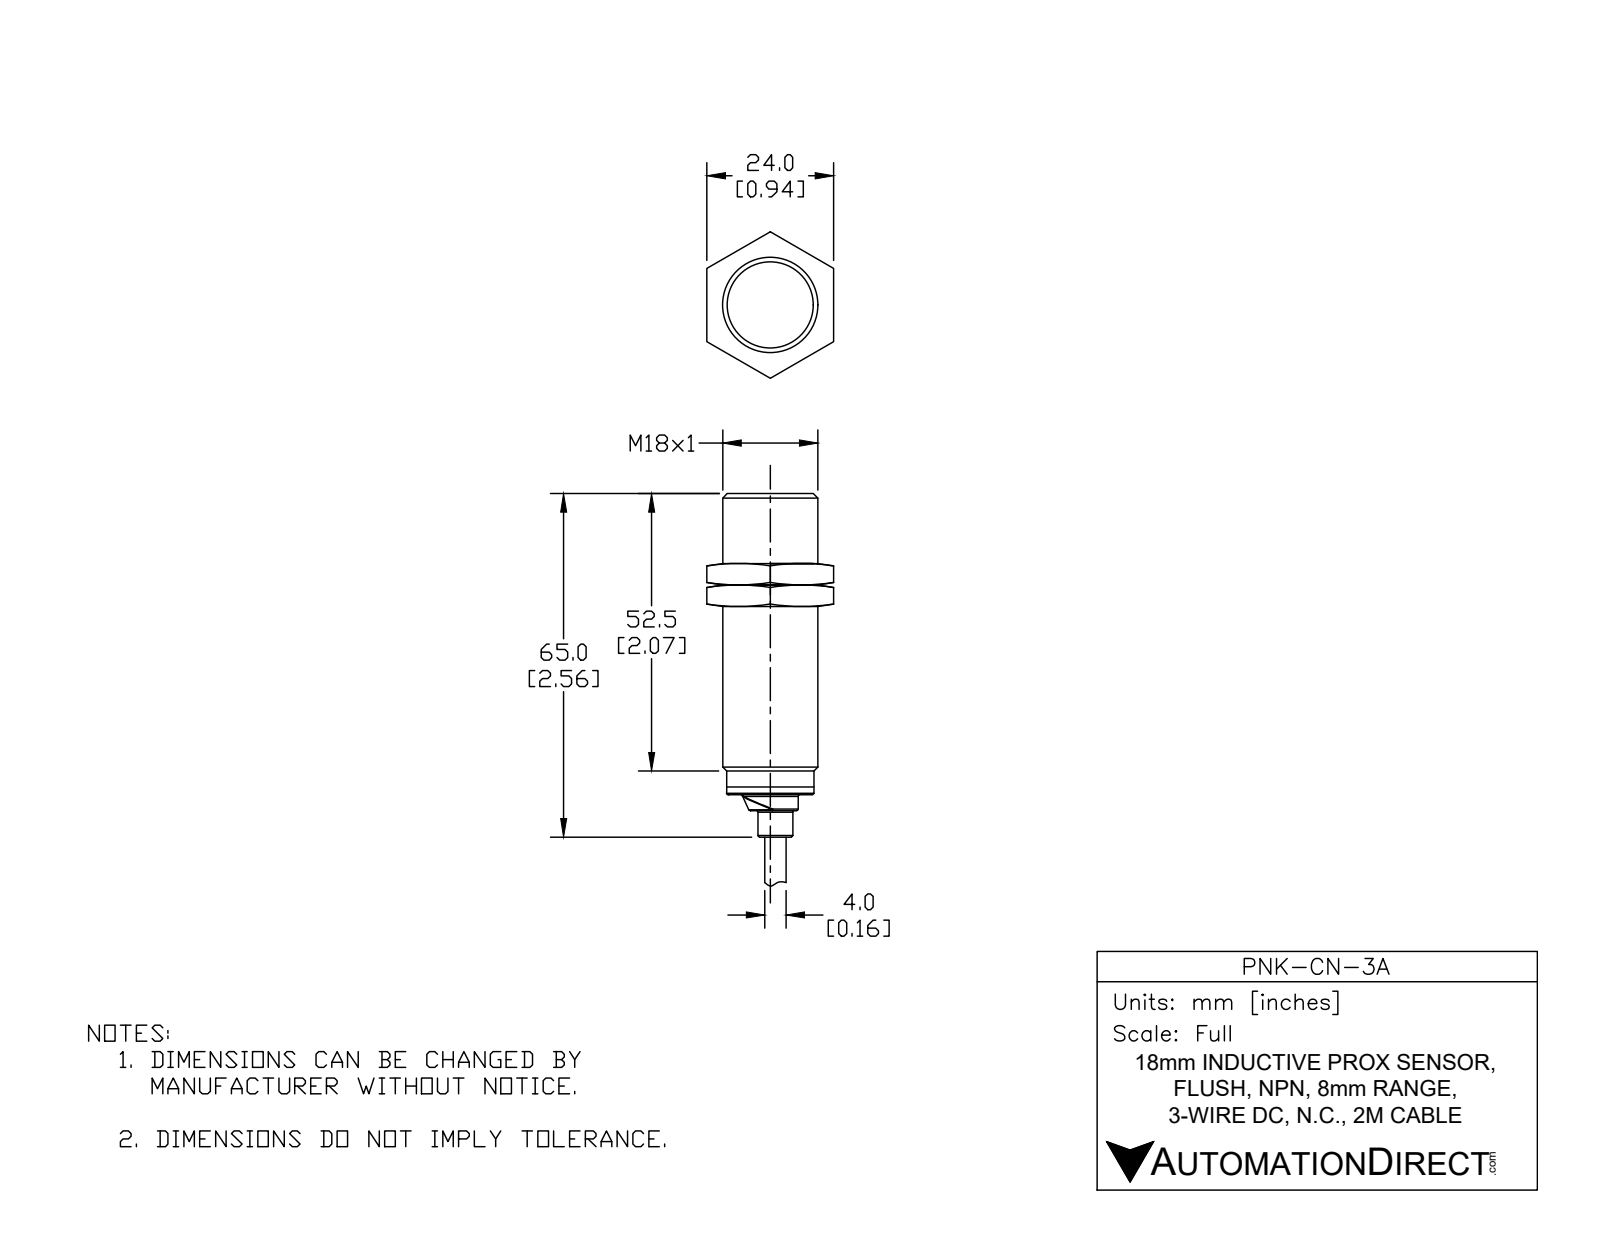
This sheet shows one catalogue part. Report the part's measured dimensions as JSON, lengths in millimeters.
{"part_name": "PNK-CN-3A", "step_written_by": "SolidWorks 2017 (AUTOMOTIVE_DESIGN)", "units": "millimeters", "bodies": {"solids": 1, "faces": 76, "planar": 18, "cylindrical": 20, "other": 38}, "overall_size": [115.8, 18, 18], "volume_mm3": 15300, "surface_area_mm2": 4577, "round_holes": [[16.1, 1]], "round_bosses_or_shafts": [[18, 1], [16.5, 1], [16.5, 1], [16.1, 1], [10.6, 1], [6.6, 1], [4, 1]], "partial_cylinders_radius": [[2, 1], [2.1, 1], [2.3, 1]], "face_to_face_distances": [57, 60, 3, 65, 8, 5, 115.8, 58.8, 55.8, 50.8]}
